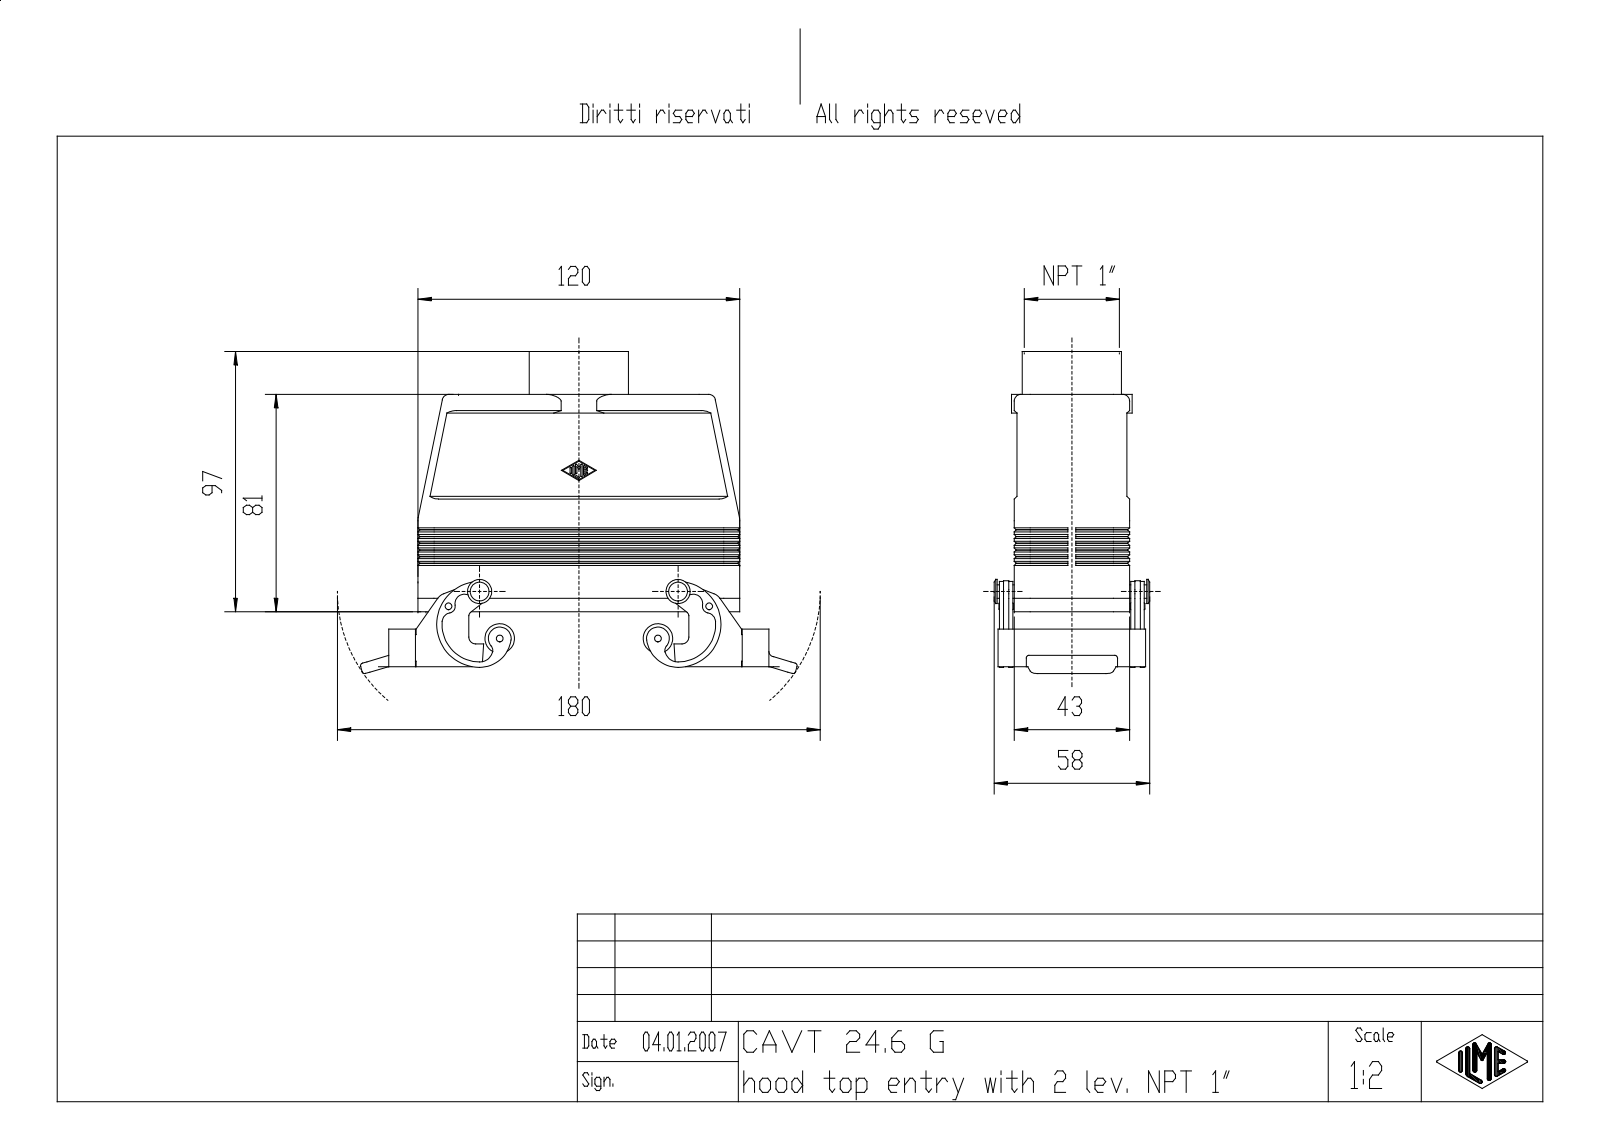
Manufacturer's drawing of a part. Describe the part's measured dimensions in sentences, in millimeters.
The part is named "MSBO15917". Its 3-D file was written by "Creo Elements/Direct Modeling 18.0B 02-Dec-2011 (C) Parametric Technology GmbH (AUTOMOTIVE_DESIGN)". It is 1 solid with 807 faces: 416 planar, 271 cylindrical and 120 other. Overall it measures 162.79 by 120.08 by 58 millimeters. Its volume is 133 060 cubic millimeters and its surface area 75 712 square millimeters. Round holes: 4 of diameter 4, 3 of diameter 2.46, 2 of diameter 2.5, 1 of diameter 2.46. Round bosses or shafts: 2 of diameter 11, 2 of diameter 9, 2 of diameter 5, 2 of diameter 2, 1 of diameter 45, 1 of diameter 37. Partial cylindrical surfaces (rounded edges, fillets, slot ends): 14 of radius 0.25, 12 of radius 1, 10 of radius 2.5, 10 of radius 6, 8 of radius 3, 7 of radius 2, 4 of radius 3.5, 4 of radius 5. The main face-to-face distances are 4, 3, 39, 35, 38, 1, 42, 43, 41, 2. The hole center spacings are 27, 104, 107.45, 97.2.
